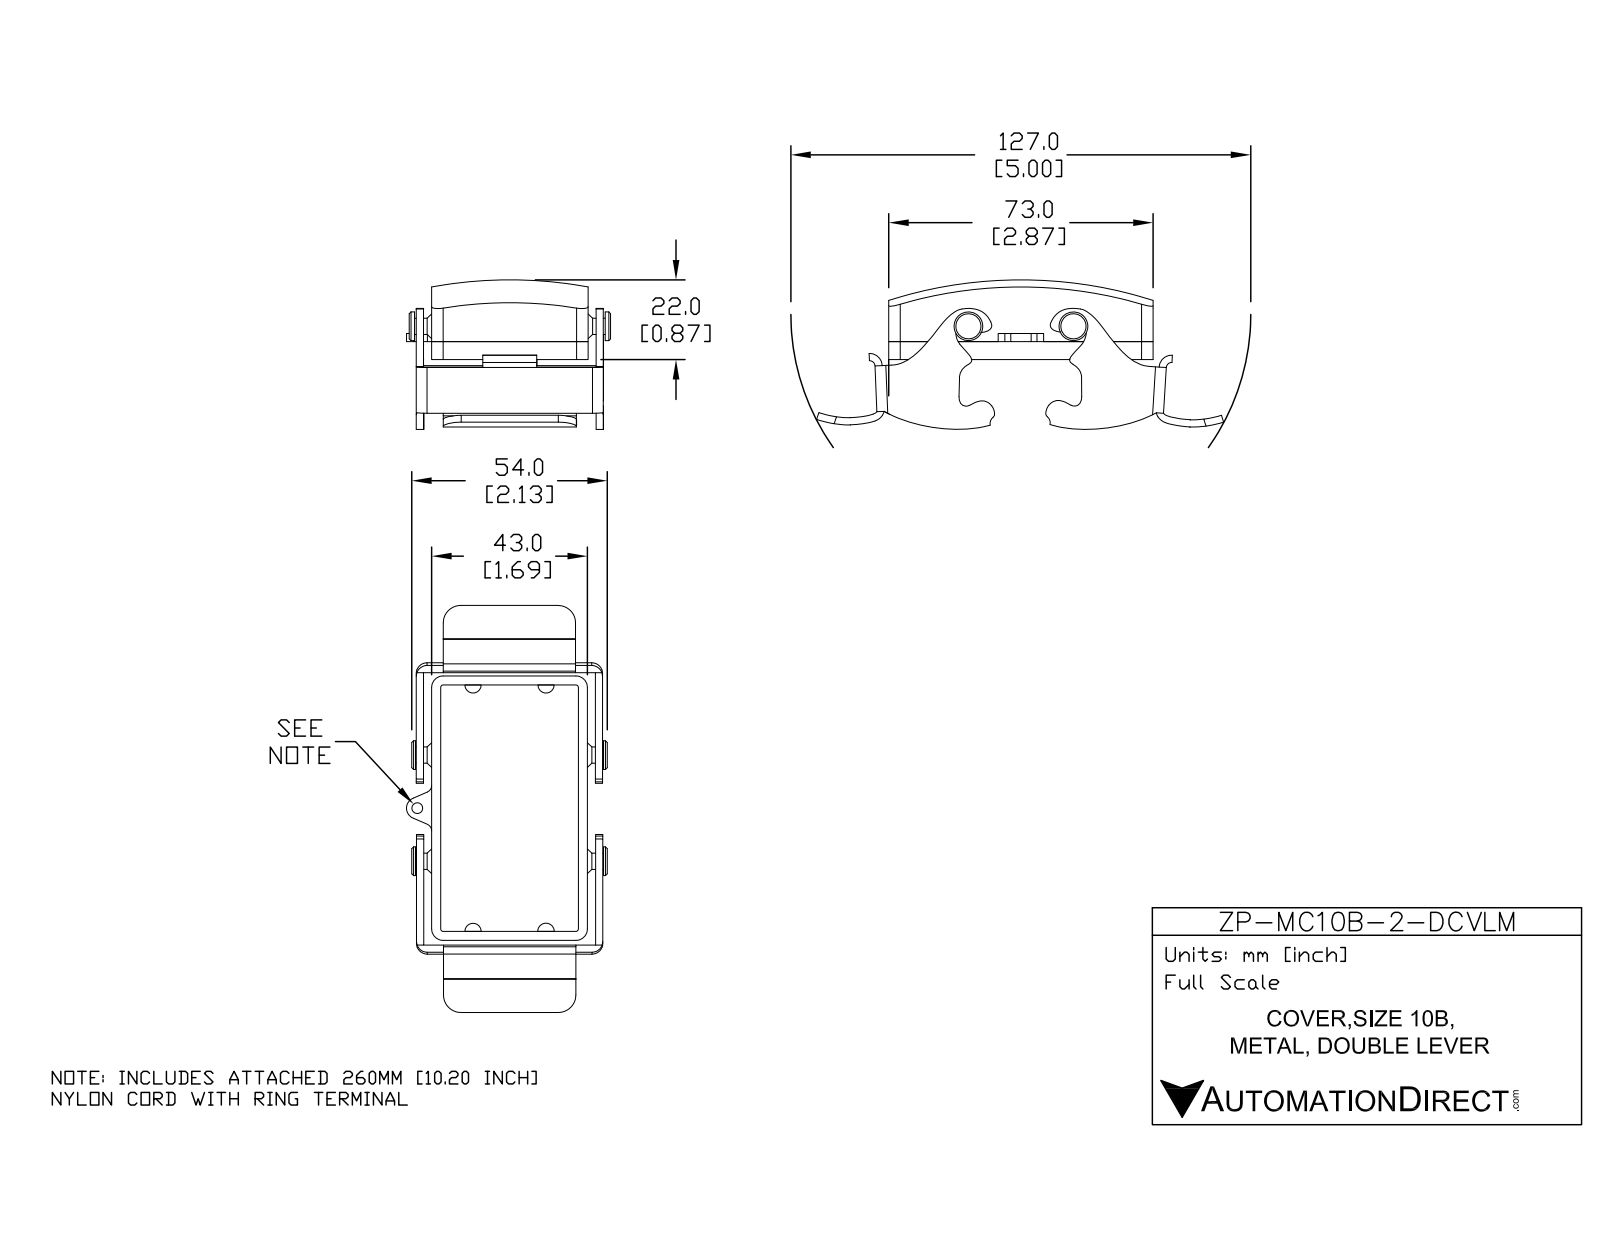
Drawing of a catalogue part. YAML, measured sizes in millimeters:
part_name: "ZP-MC10B-2-DCVLM"
step_written_by: "SolidWorks 2011 (AUTOMOTIVE_DESIGN)"
units: millimeters
bodies: {solids: 4, faces: 240, planar: 102, cylindrical: 128, other: 10}
overall_size: [117.93, 56.75, 28.82]
volume: 21354
surface_area: 24011
round_holes:
  - {diameter: 3, count: 1}
round_bosses_or_shafts:
  - {diameter: 8, count: 2}
  - {diameter: 4.52, count: 2}
partial_cylinders:
  - {radius: 1, count: 16}
  - {radius: 0.5, count: 8}
  - {radius: 2, count: 8}
  - {radius: 0.7, count: 4}
  - {radius: 3.2, count: 4}
  - {radius: 4, count: 4}
  - {radius: 2.25, count: 3}
  - {radius: 3, count: 3}
face_to_face_distances: [1, 2.5, 45.5, 41, 44.5, 3.5, 42, 2, 4.5, 43]
